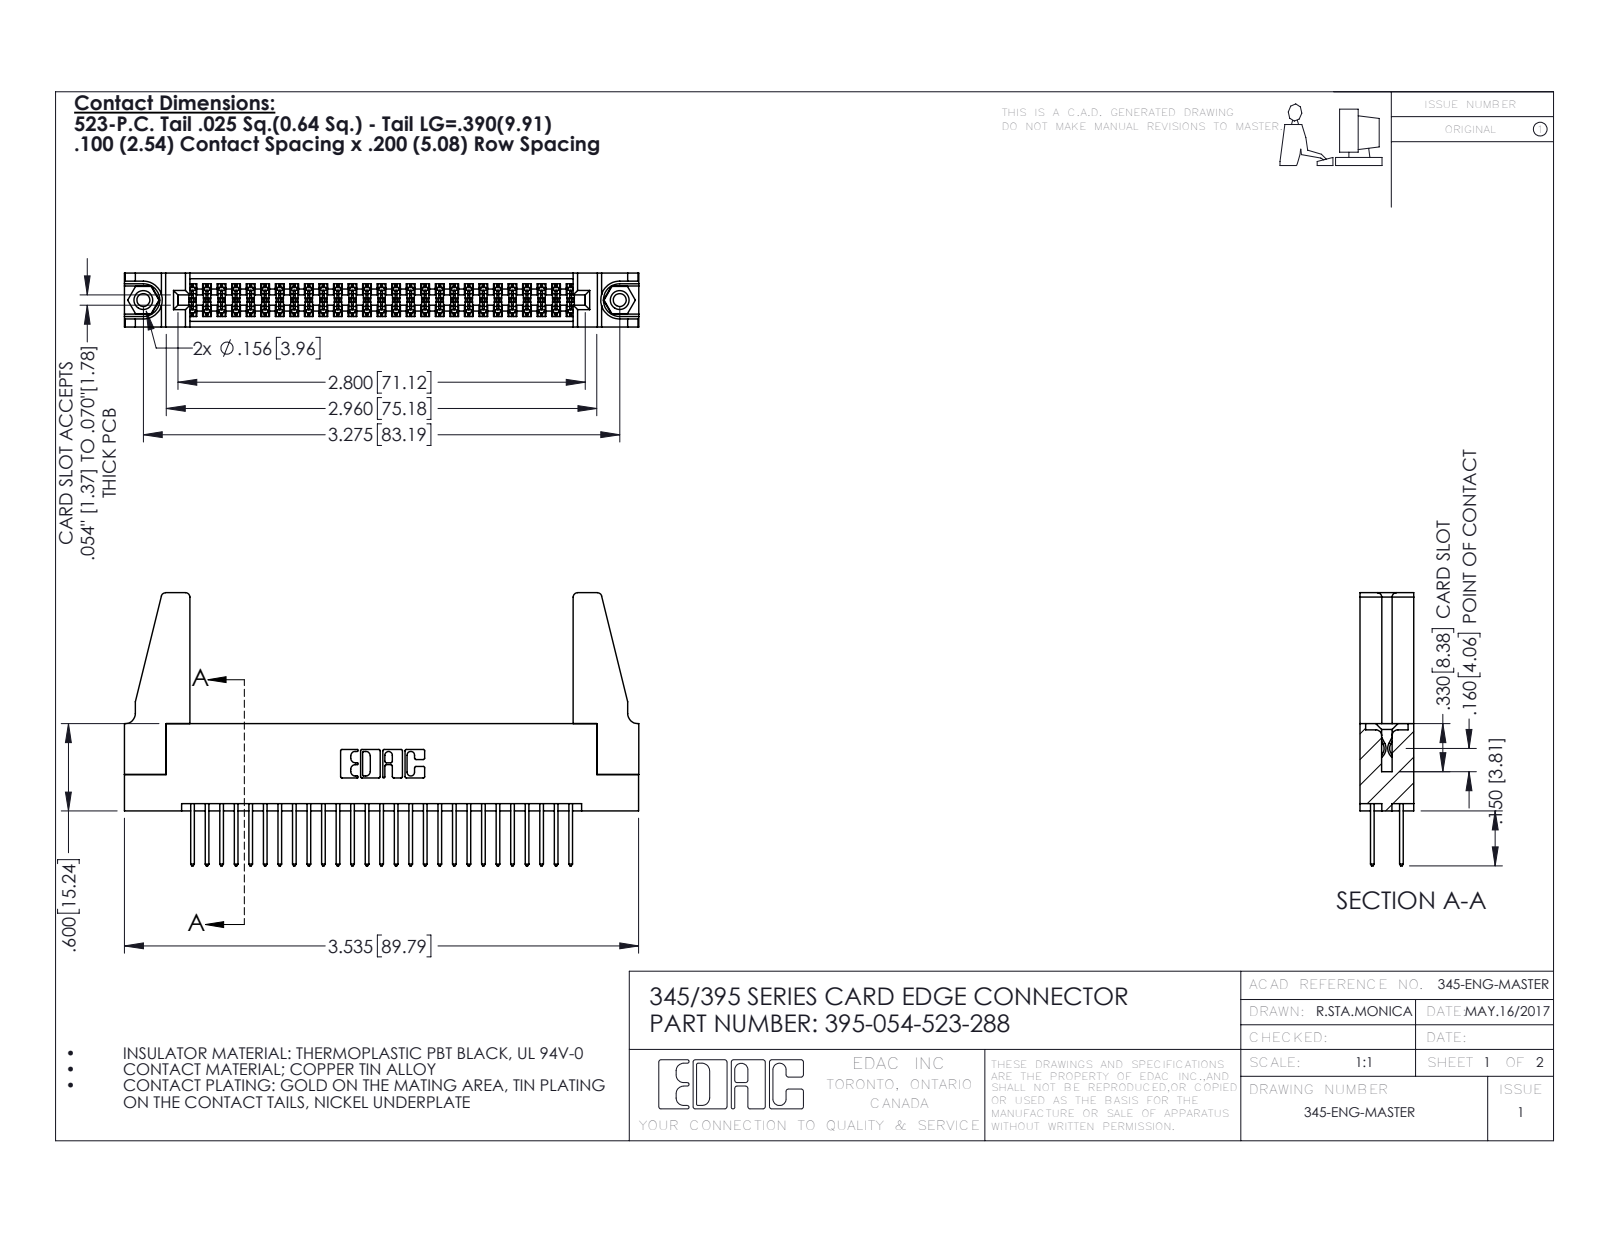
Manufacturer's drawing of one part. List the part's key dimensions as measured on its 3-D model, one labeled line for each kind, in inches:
Part name (STEP PRODUCT): 345 Part_Flush Mounting Lugs - 0.156 Dia-TH; 345-292-001_345-293-123; 395-054-523-288; 345-250-001_345-250-001-102 (+1 more)
STEP written by: SolidWorks 2016 (CONFIG_CONTROL_DESIGN)
Units: inches
Bodies: 59 solids, 2950 faces (1934 planar, 1000 cylindrical, 16 other)
Overall size (bounding box): 3.536 × 1.877 × 0.37
Volume: 0.729 in³ · Surface area: 25.08 in²
Round holes (diameter × count): ⌀0.089 ×2, ⌀0.125 ×2, ⌀0.156 ×2, ⌀0.064 ×1
Round bosses / shafts (diameter × count): ⌀0.155 ×2
Partial cylindrical surfaces — rounded edges, fillets, slot ends (radius × count): R0.006 ×81, R0.01 ×54, R0.01 ×22, R0.03 ×8, R0.007 ×6, R0.031 ×6, R0.026 ×3, R0.014 ×2
Main face-to-face distances: 0.072, 0.298, 0.37, 0.2, 0.098, 0.272, 0.025, 0.225, 0.175, 0.149
Hole centre spacings: 0.27, 3.04, 3.275
